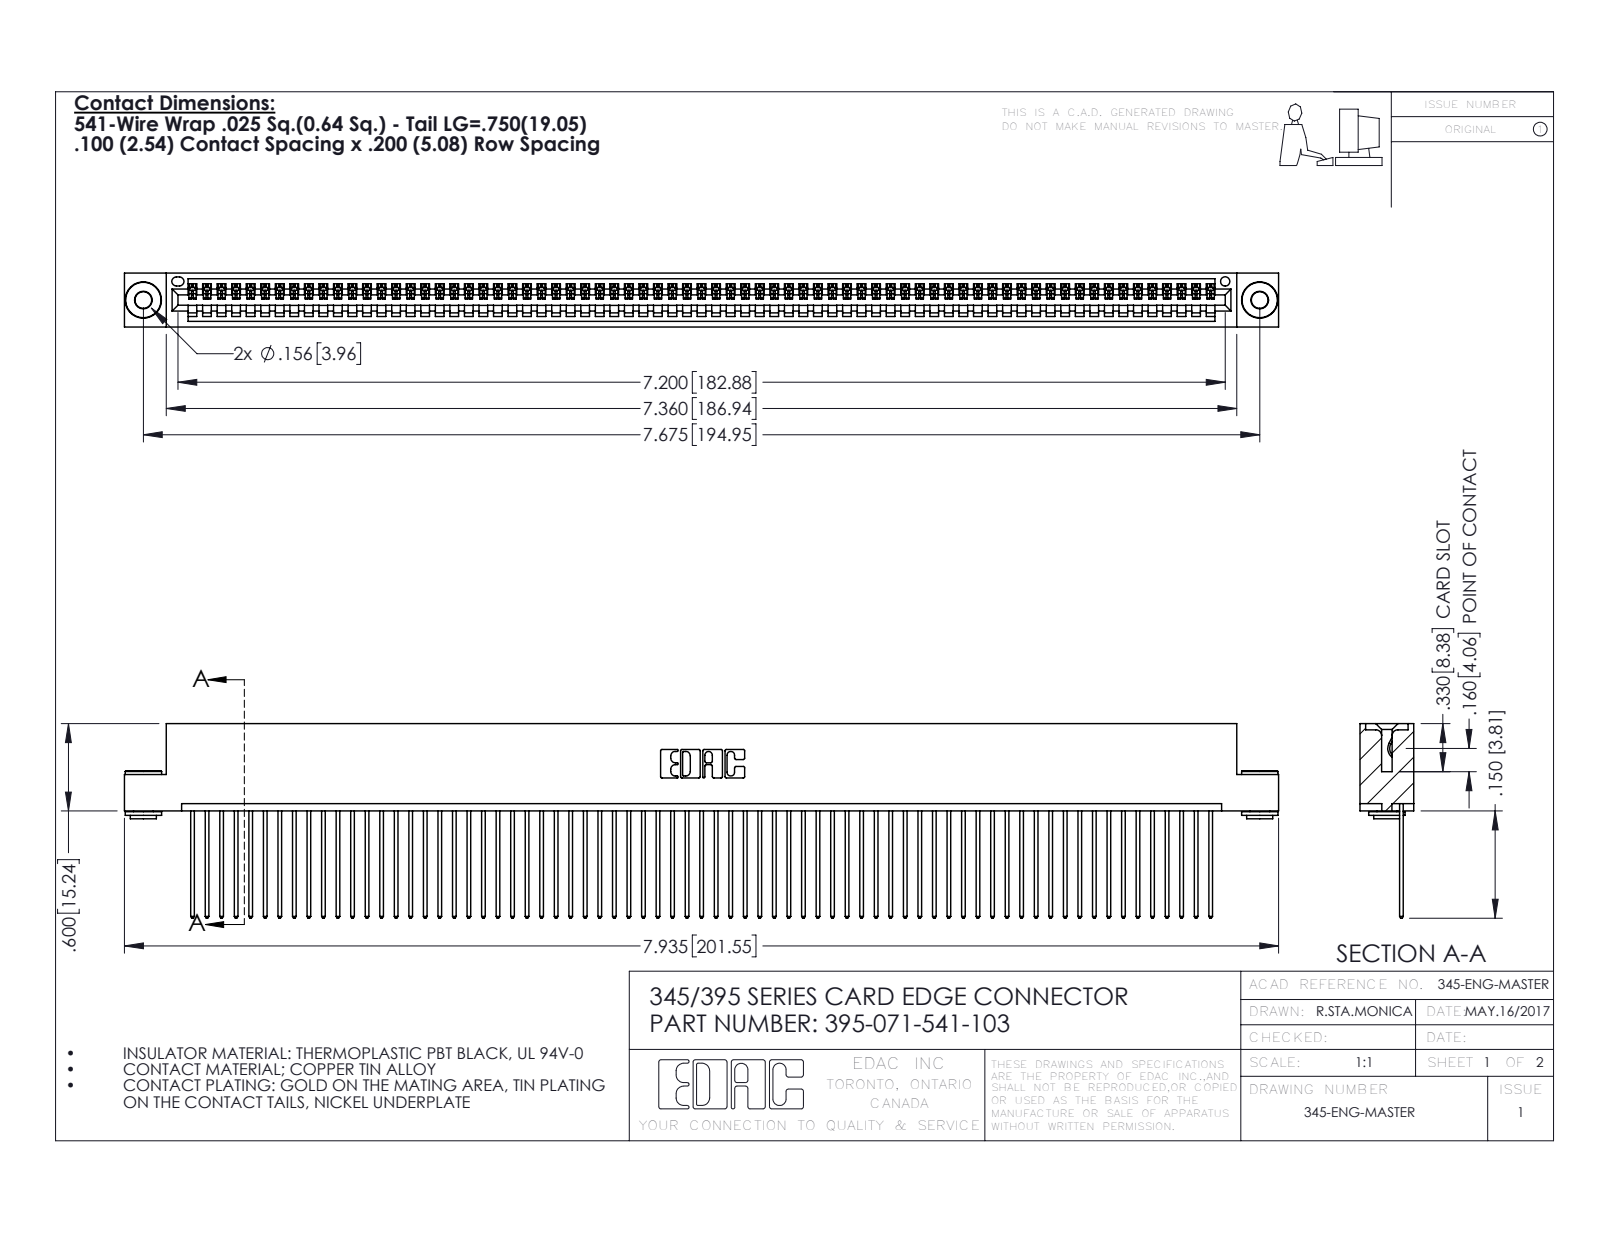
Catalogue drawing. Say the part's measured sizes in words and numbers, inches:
The part is named "345-250-002_345-250-002-102; 345 Part_Flush Mounting Lugs - 0.156 Dia-TH; 345-292-001_345-293-141; 395-071-541-103". Its 3-D file was written by "SolidWorks 2016 (CONFIG_CONTROL_DESIGN)". It is 74 solids with 4282 faces: 2930 planar, 1344 cylindrical and 8 other. Overall it measures 7.935 by 1.337 by 0.37 inches. Its volume is 1.198 cubic inches and its surface area 43.52 square inches. Round holes: 2 of diameter 0.116, 2 of diameter 0.156, 1 of diameter 0.064. Round bosses or shafts: 2 of diameter 0.25, 2 of diameter 0.18, 2 of diameter 0.136. Partial cylindrical surfaces (rounded edges, fillets, slot ends): 142 of radius 0.006, 142 of radius 0.01, 22 of radius 0.01, 6 of radius 0.007, 6 of radius 0.031, 3 of radius 0.026, 2 of radius 0.031, 2 of radius 0.04. The main face-to-face distances are 0.072, 0.298, 0.025, 0.098, 0.272, 0.37, 0.2, 0.225, 0.149, 0.072. The hole center spacings are 0.27, 7.439, 7.675.
